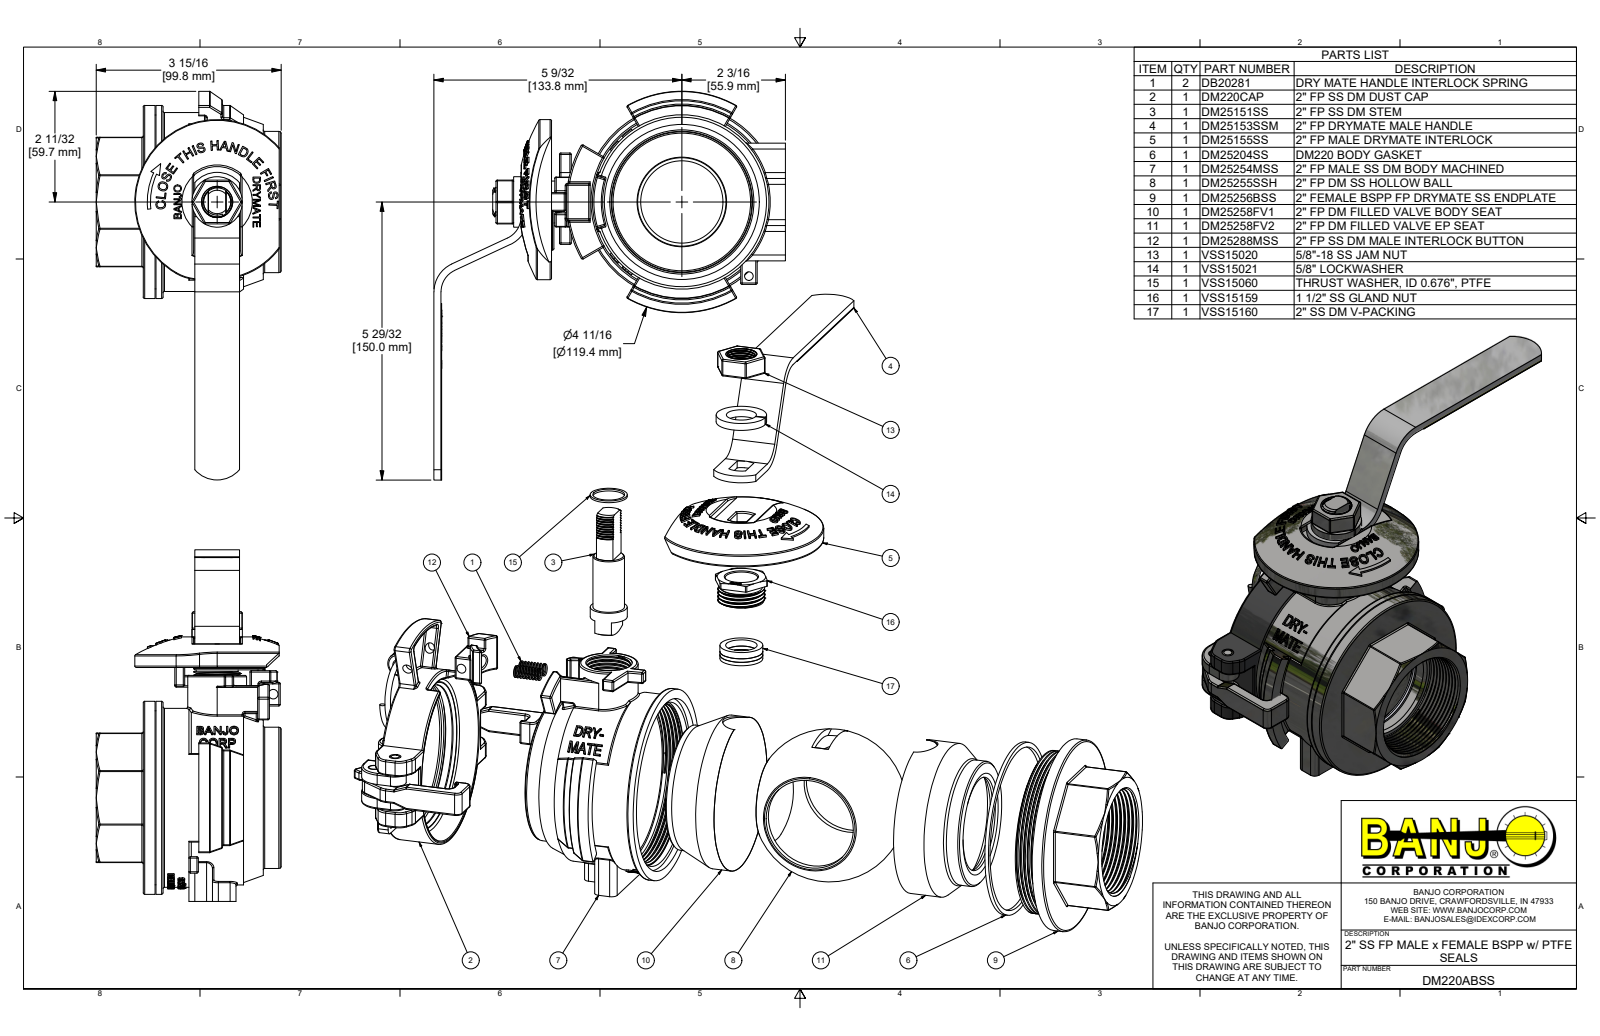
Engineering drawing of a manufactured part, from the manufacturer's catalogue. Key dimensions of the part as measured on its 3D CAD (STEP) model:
Part name (STEP PRODUCT): DM220ABSS; DM220ABSSX; DM25254MSS; DB20281 (+8 more)
STEP written by: Autodesk Inventor 2022 (AUTOMOTIVE_DESIGN)
Units: inches
Bodies: 22 solids, 2510 faces (856 planar, 521 cylindrical, 1133 other)
Overall size (bounding box): 8.255 × 7.468 × 3.93
Volume: 25.42 in³ · Surface area: 339.8 in²
Round holes (diameter × count): ⌀0.18 ×1, ⌀0.2 ×1, ⌀0.64 ×1, ⌀0.662 ×1, ⌀0.67 ×1, ⌀0.676 ×1, ⌀0.69 ×1, ⌀0.84 ×1, ⌀0.876 ×1, ⌀0.92 ×1, ⌀1 ×1, ⌀1.9 ×1
Round bosses / shafts (diameter × count): ⌀4.1 ×1, ⌀3.8 ×1, ⌀3.7 ×1, ⌀3.693 ×1, ⌀3.49 ×1, ⌀3.399 ×1, ⌀3.29 ×1, ⌀3 ×1
Partial cylindrical surfaces — rounded edges, fillets, slot ends (radius × count): R0.03 ×222, R0.125 ×8, R0.65 ×3, R0.06 ×2, R0.135 ×2, R0.4 ×2, R0.5 ×2, R0.625 ×2
Main face-to-face distances: 0.15, 0.16, 0.5, 2.5, 2.75, 2.77, 2.93, 0.25, 1.85, 0.11
Hole centre spacings: 2.124, 2.502
